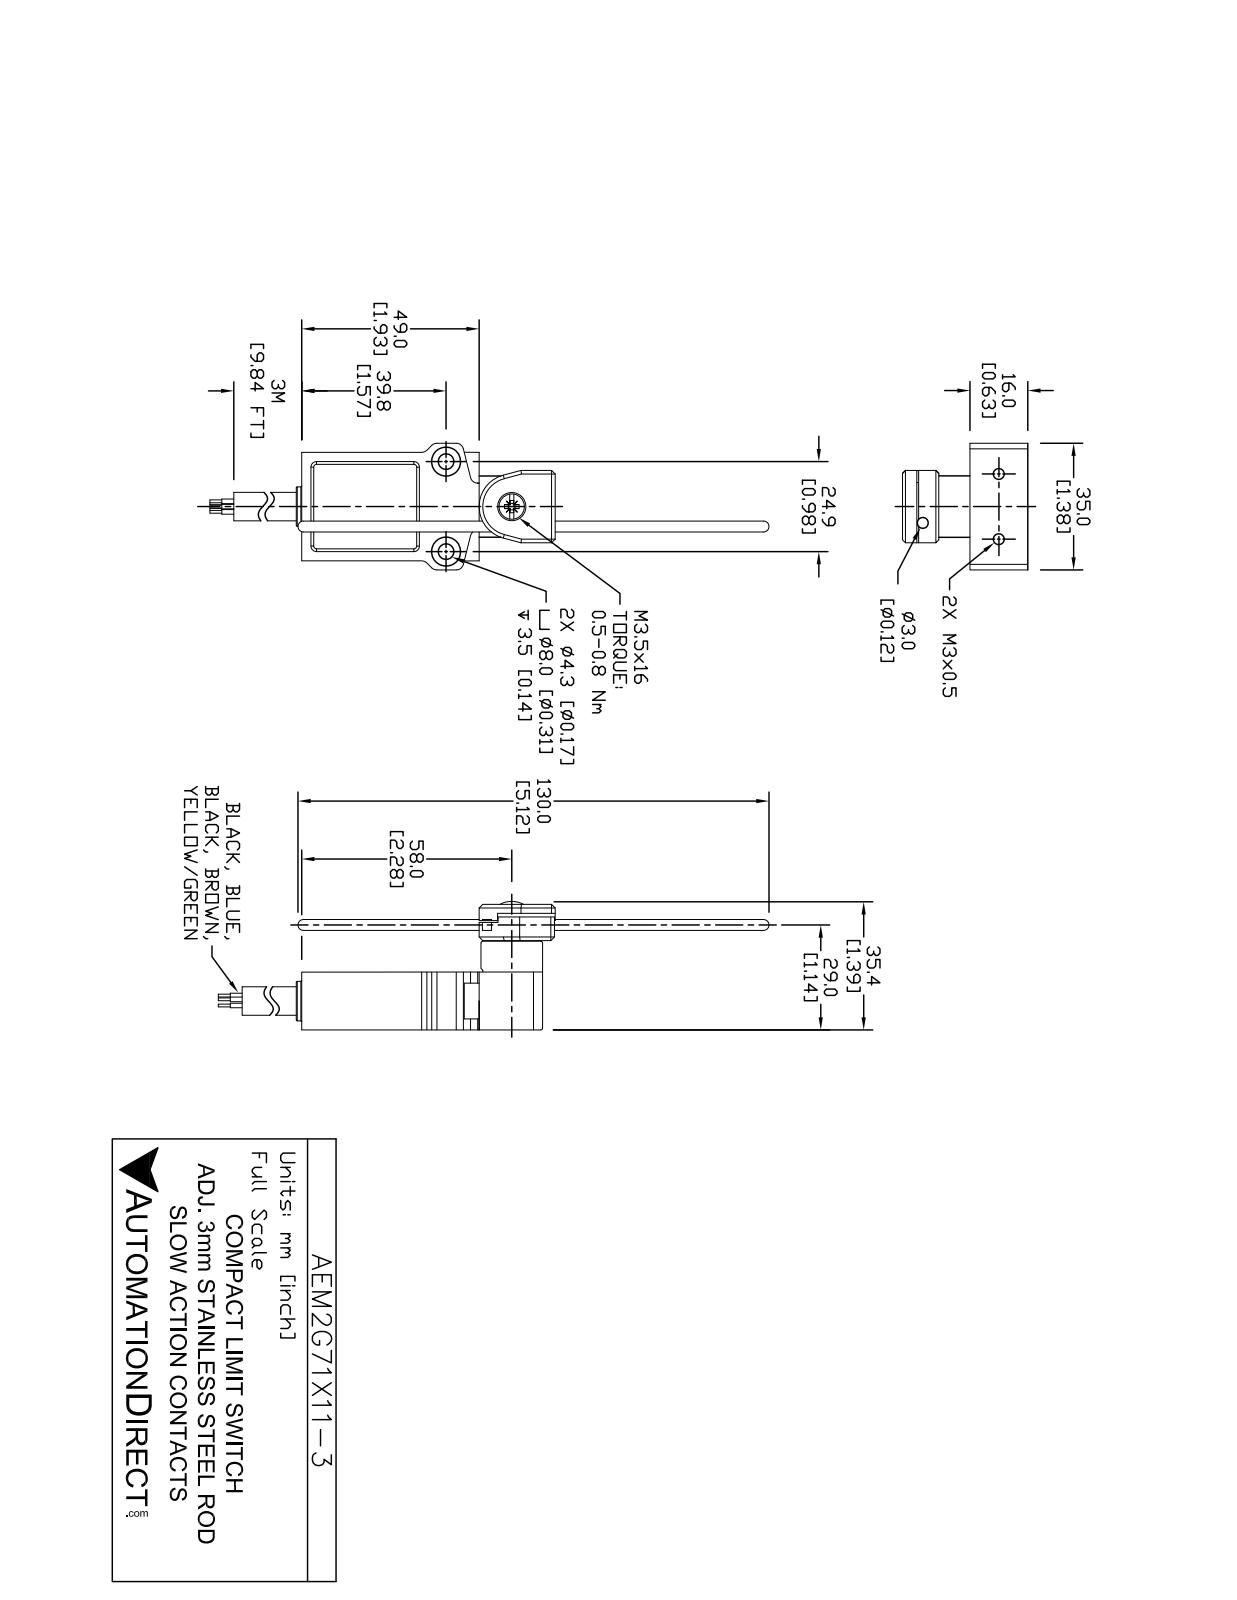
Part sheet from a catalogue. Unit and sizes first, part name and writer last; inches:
Units: inches
Overall size (bounding box): 5.634 × 1.378 × 1.374
Round holes (diameter × count): ⌀0.118 ×2, ⌀0.173 ×2, ⌀0.323 ×2, ⌀0.197 ×1, ⌀0.32 ×1
Round bosses / shafts (diameter × count): ⌀0.622 ×1, ⌀0.289 ×1, ⌀0.276 ×1, ⌀0.12 ×1
Partial cylindrical surfaces — rounded edges, fillets, slot ends (radius × count): R0.079 ×8, R0.256 ×1, R0.355 ×1
Main face-to-face distances: 0.63, 1.181, 0.354, 1.929, 0.984, 0.185, 0.18, 0.534, 1.164, 0.539
Hole centre spacings: 0.863, 0.748, 0.984
Volume: 1.979 in³ · Surface area: 18.36 in²
Bodies: 3 solids, 144 faces (91 planar, 43 cylindrical, 10 other)
Part name (STEP PRODUCT): AEM2G71X11-3_Default
STEP written by: SolidWorks 2021 (CONFIG_CONTROL_DESIGN)
